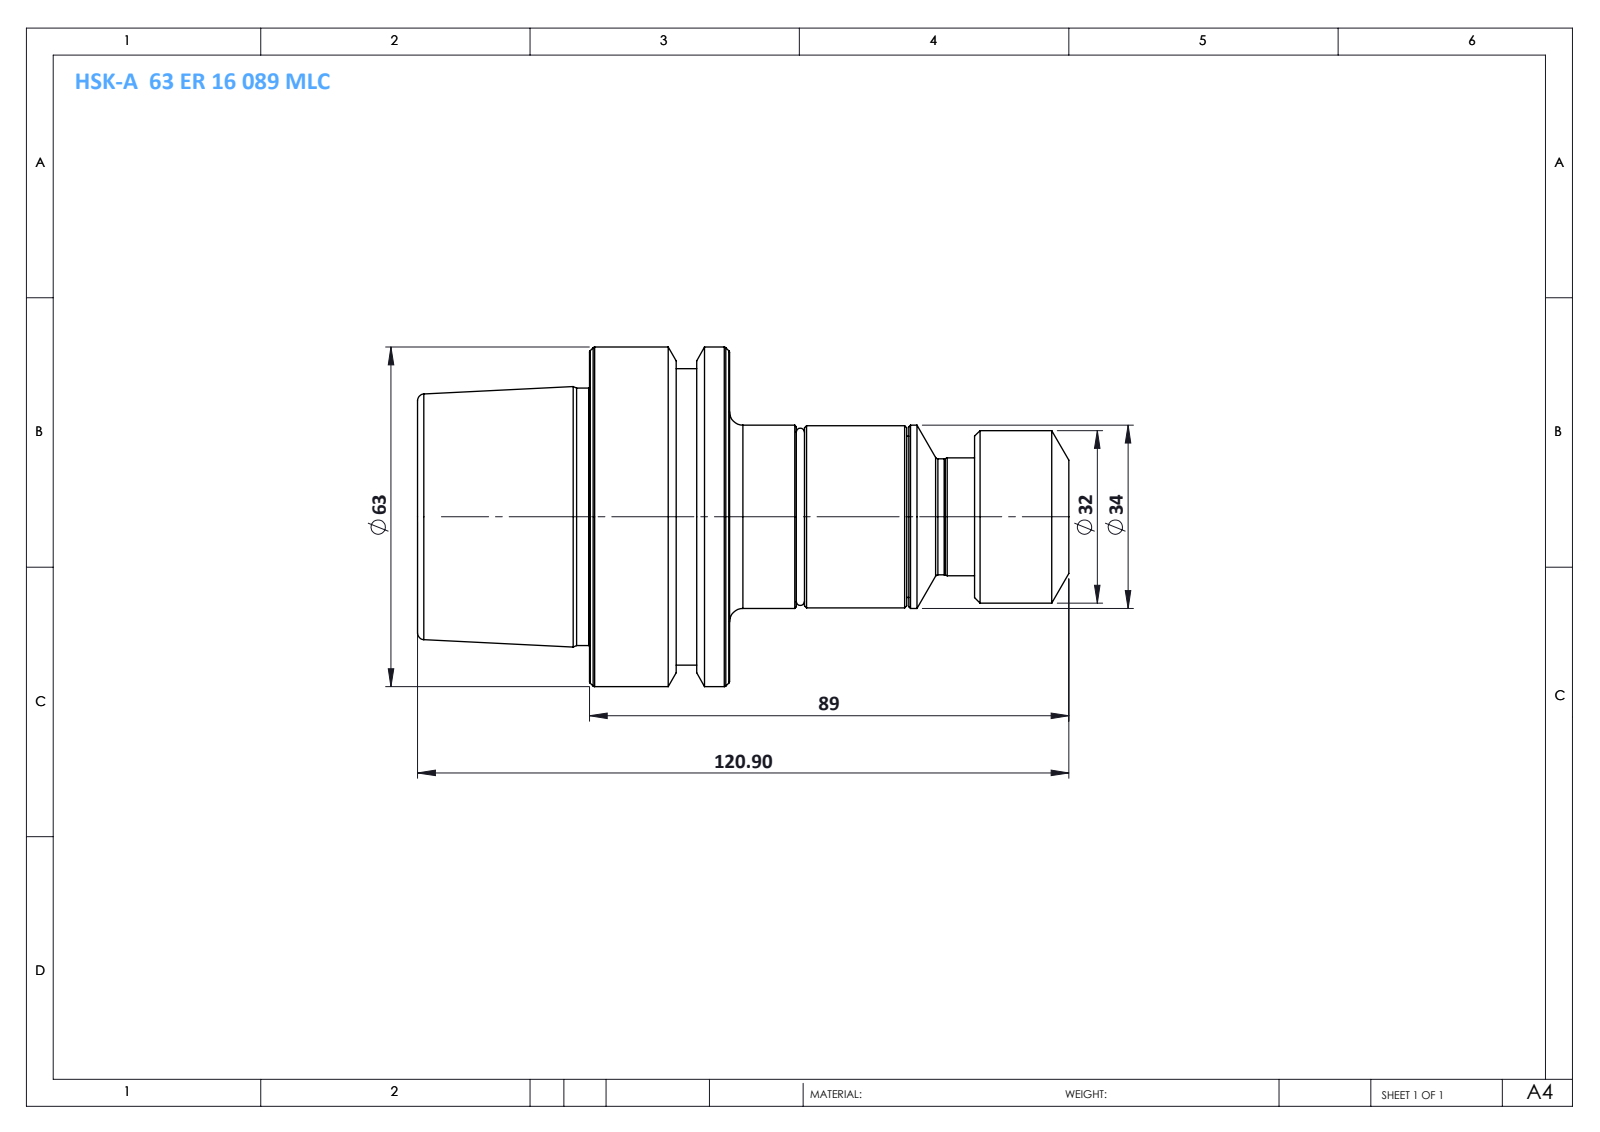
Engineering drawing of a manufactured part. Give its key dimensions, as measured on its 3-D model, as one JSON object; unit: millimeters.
{"part_name": "HSK-A 63 ER 16 089 MLC", "step_written_by": "SolidWorks 2014 (CONFIG_CONTROL_DESIGN)", "units": "millimeters", "bodies": {"solids": 1, "faces": 83, "planar": 11, "cylindrical": 22, "other": 50}, "overall_size": [120.9, 63, 63], "volume_mm3": 182003, "surface_area_mm2": 23772, "round_bosses_or_shafts": [[63, 1], [55, 1], [47.78, 1], [34, 1], [33.8, 1], [32, 1], [29.9, 1], [21.9, 1]], "face_to_face_distances": [57.9, 26, 31.9, 63, 89, 120.9, 17.5, 45.5, 71.5, 103.4]}
